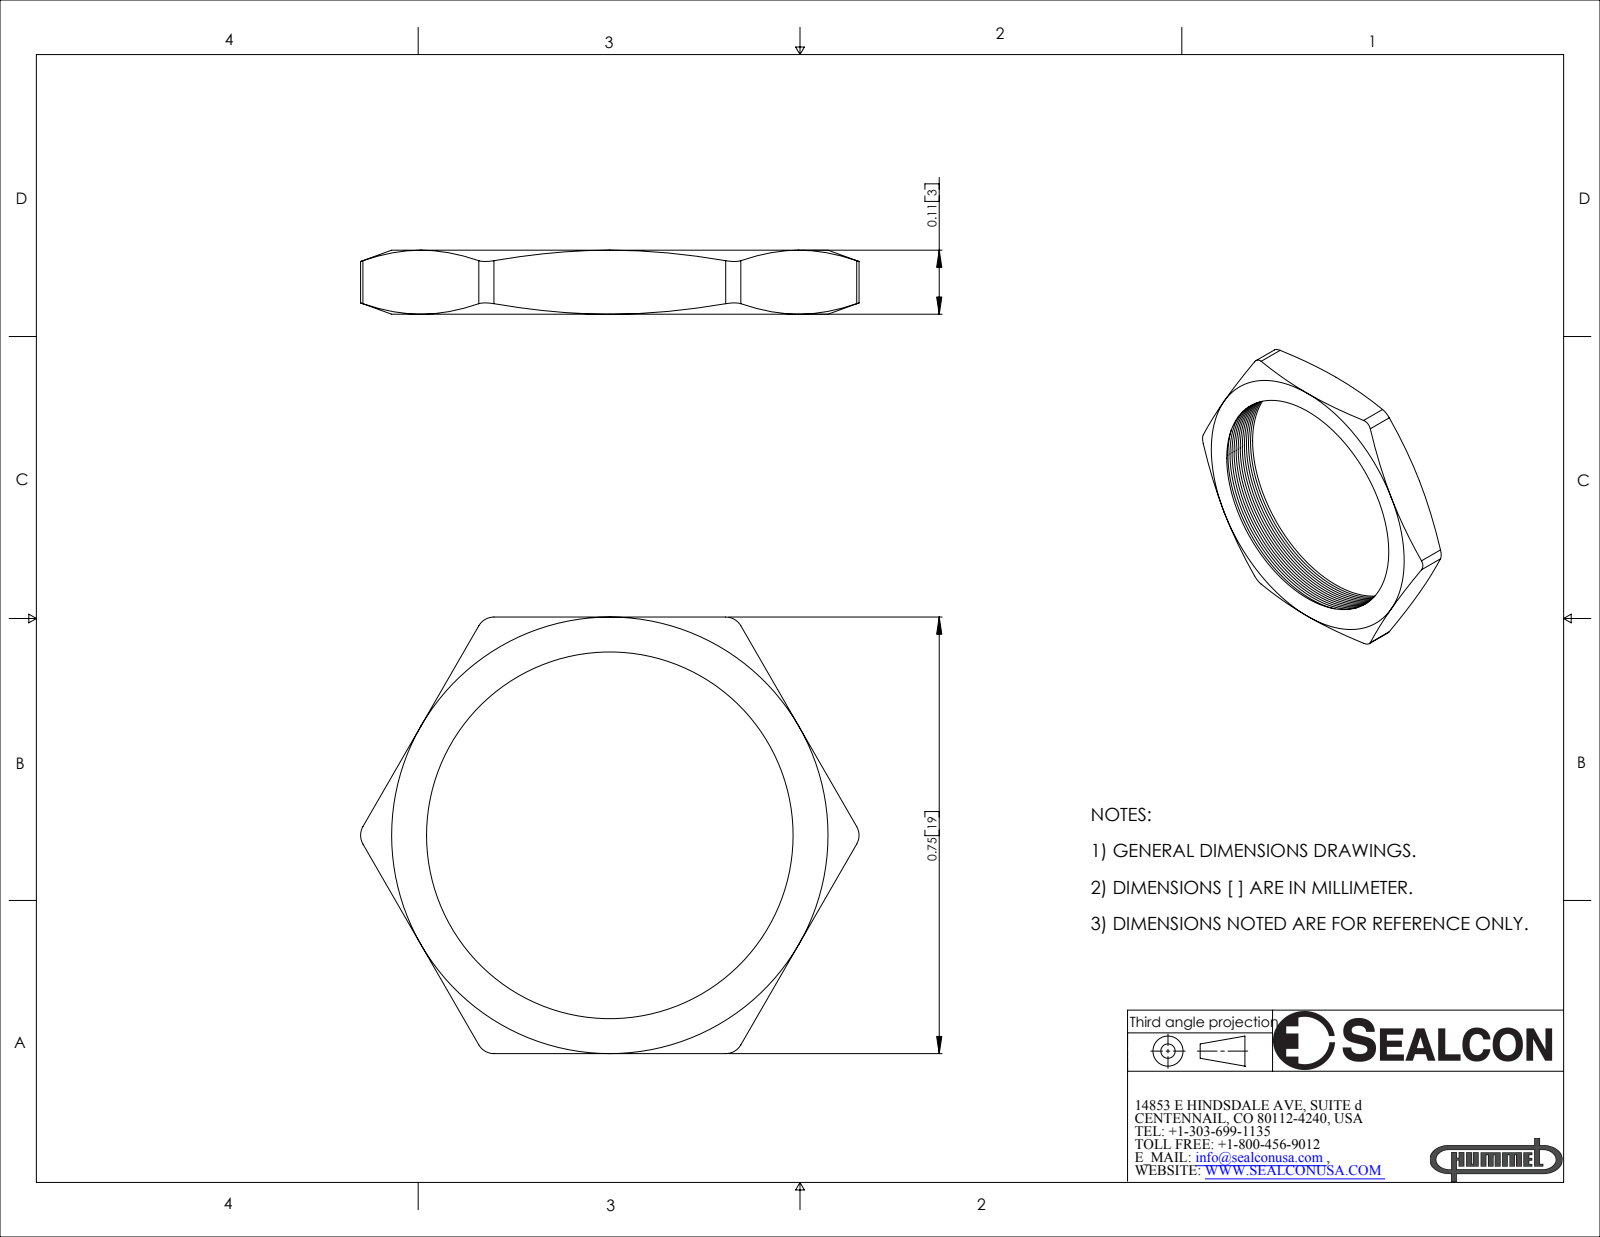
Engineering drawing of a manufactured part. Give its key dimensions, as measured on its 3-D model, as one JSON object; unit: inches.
{"part_name": "NM-16-BR", "step_written_by": "SolidWorks 2007 (CONFIG_CONTROL_DESIGN)", "units": "inches", "bodies": {"solids": 1, "faces": 83, "planar": 8, "cylindrical": 7, "other": 68}, "overall_size": [0.857, 0.75, 0.11], "volume_in3": 0.016, "surface_area_in2": 1.033, "partial_cylinders_radius": [[0.03, 6]], "face_to_face_distances": [0.11, 0.75, 0.75]}
